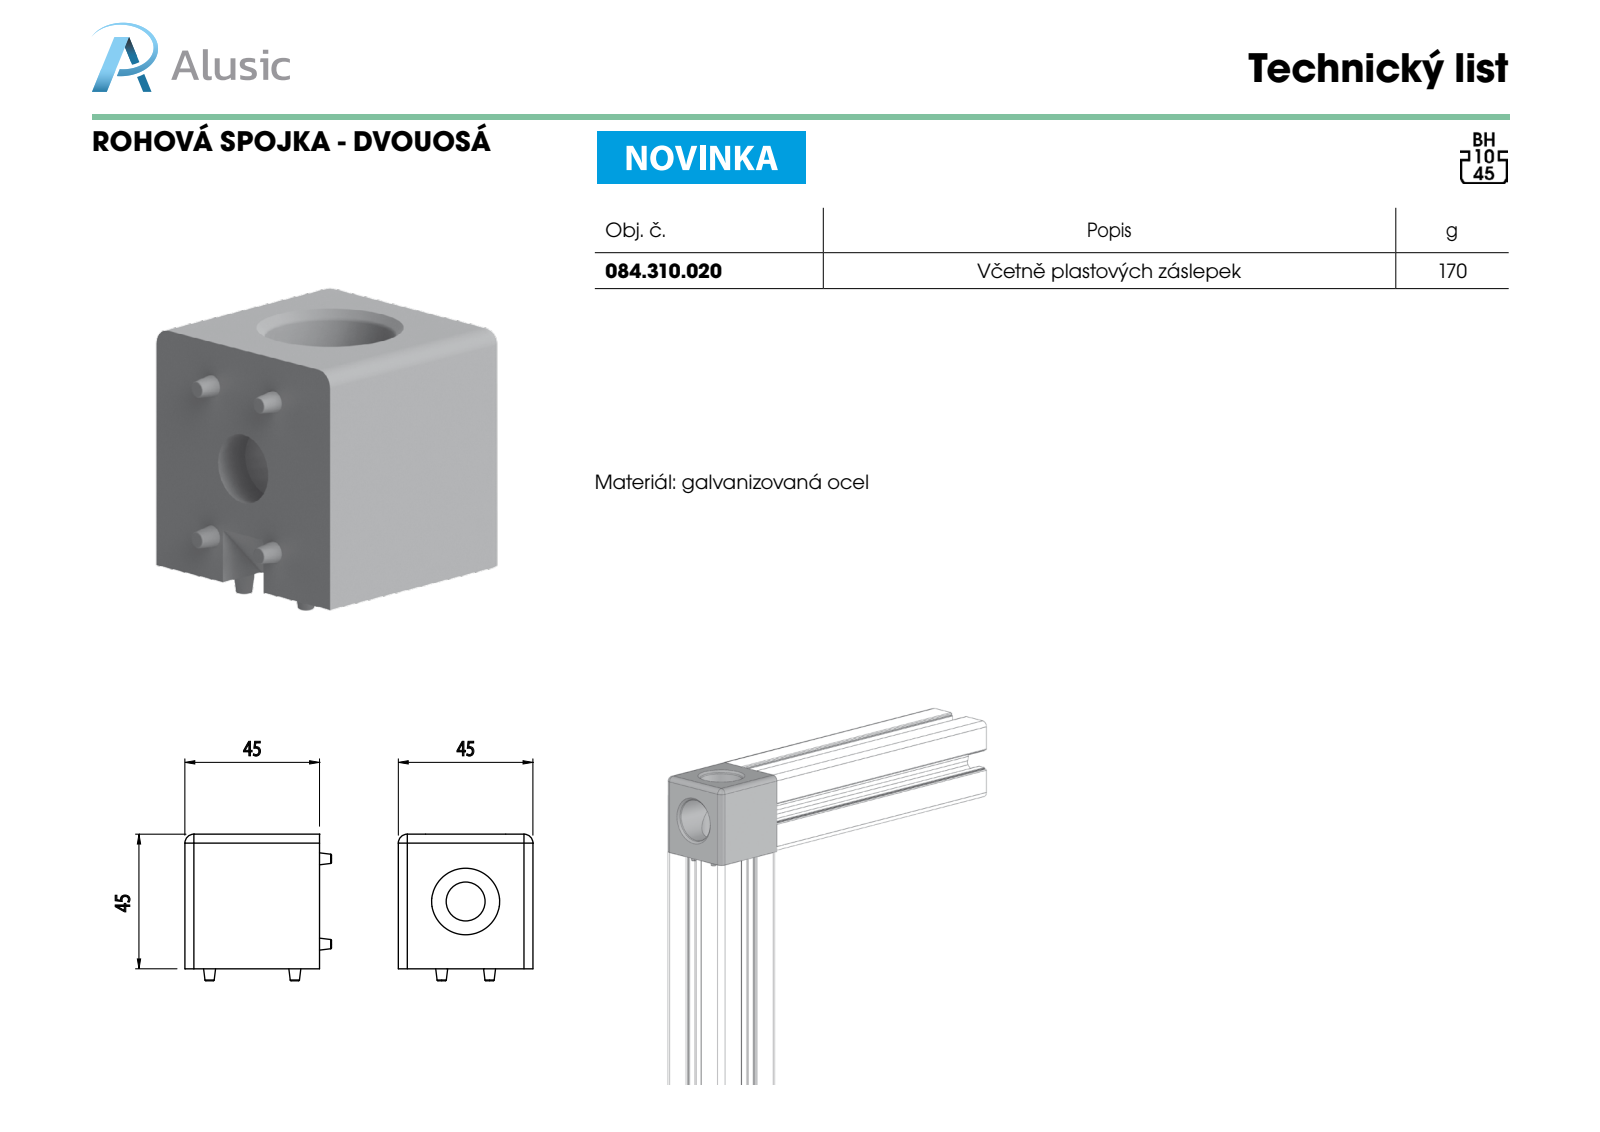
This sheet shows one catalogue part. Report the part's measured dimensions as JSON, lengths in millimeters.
{"part_name": "084.310.020", "step_written_by": "SolidWorks 2011 (CONFIG_CONTROL_DESIGN)", "units": "millimeters", "bodies": {"solids": 1, "faces": 78, "planar": 19, "cylindrical": 9, "other": 50}, "overall_size": [49, 49, 45], "volume_mm3": 64756, "surface_area_mm2": 15371, "round_holes": [[13, 2]], "partial_cylinders_radius": [[3, 5]], "face_to_face_distances": [45, 38, 7, 17.25, 27.75, 10.5, 49, 11, 4]}
